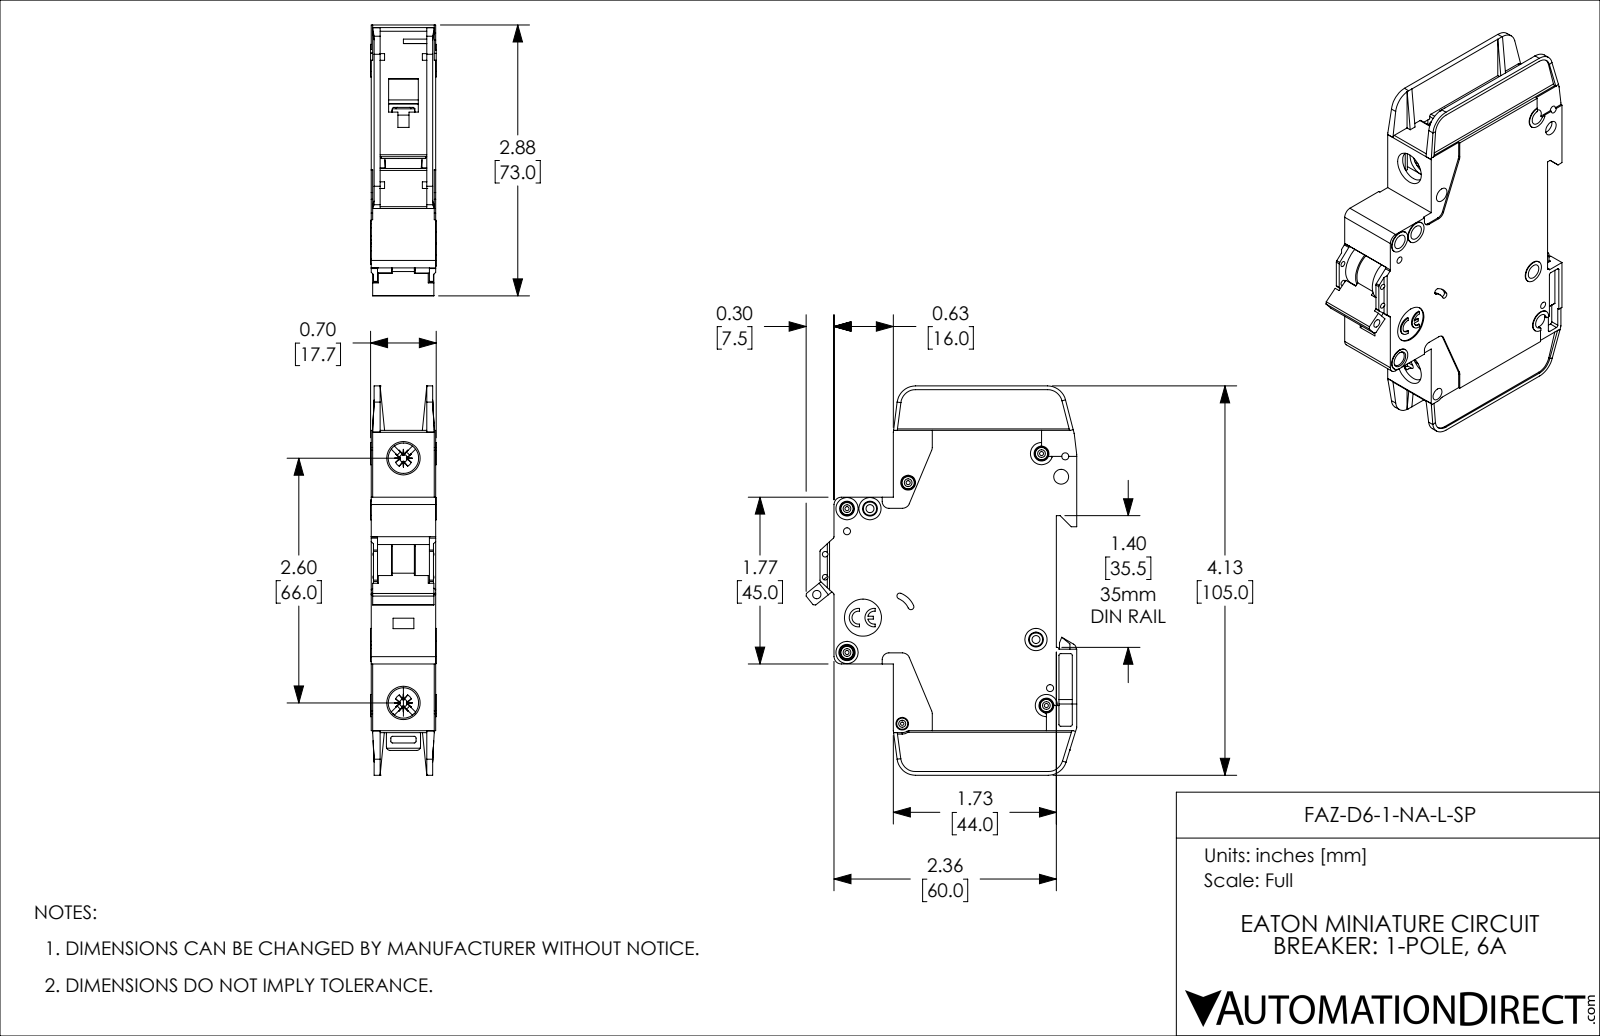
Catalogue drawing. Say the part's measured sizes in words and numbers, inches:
The part is named "FAZ-D6-1-NA-L-SP". Its 3-D file was written by "SolidWorks 2019 (AUTOMOTIVE_DESIGN)". It is 1 solid with 1127 faces: 671 planar, 357 cylindrical and 99 other. Overall it measures 4.134 by 2.876 by 0.697 inches. Its volume is 4.682 cubic inches and its surface area 41.01 square inches. Round holes: 8 of diameter 0.157, 5 of diameter 0.043, 4 of diameter 0.075, 2 of diameter 0.059, 2 of diameter 0.085, 2 of diameter 0.323, 1 of diameter 0.035, 1 of diameter 0.089, 1 of diameter 0.098, 1 of diameter 0.134, 1 of diameter 0.394. Round bosses or shafts: 5 of diameter 0.13, 4 of diameter 0.236, 2 of diameter 0.118, 1 of diameter 0.098. Partial cylindrical surfaces (rounded edges, fillets, slot ends): 42 of radius 0.02, 10 of radius 0.016, 10 of radius 0.039, 8 of radius 0.079, 5 of radius 0.197, 4 of radius 0.008, 4 of radius 0.026, 4 of radius 0.043. The main face-to-face distances are 0.047, 0.685, 0.591, 0.638, 0.094, 0.543, 0.016, 0.031, 0.496, 0.575. The hole center spacings are 0.244, 0.537, 0.87, 0.189, 0.199, 0.204, 0.221, 0.24.
